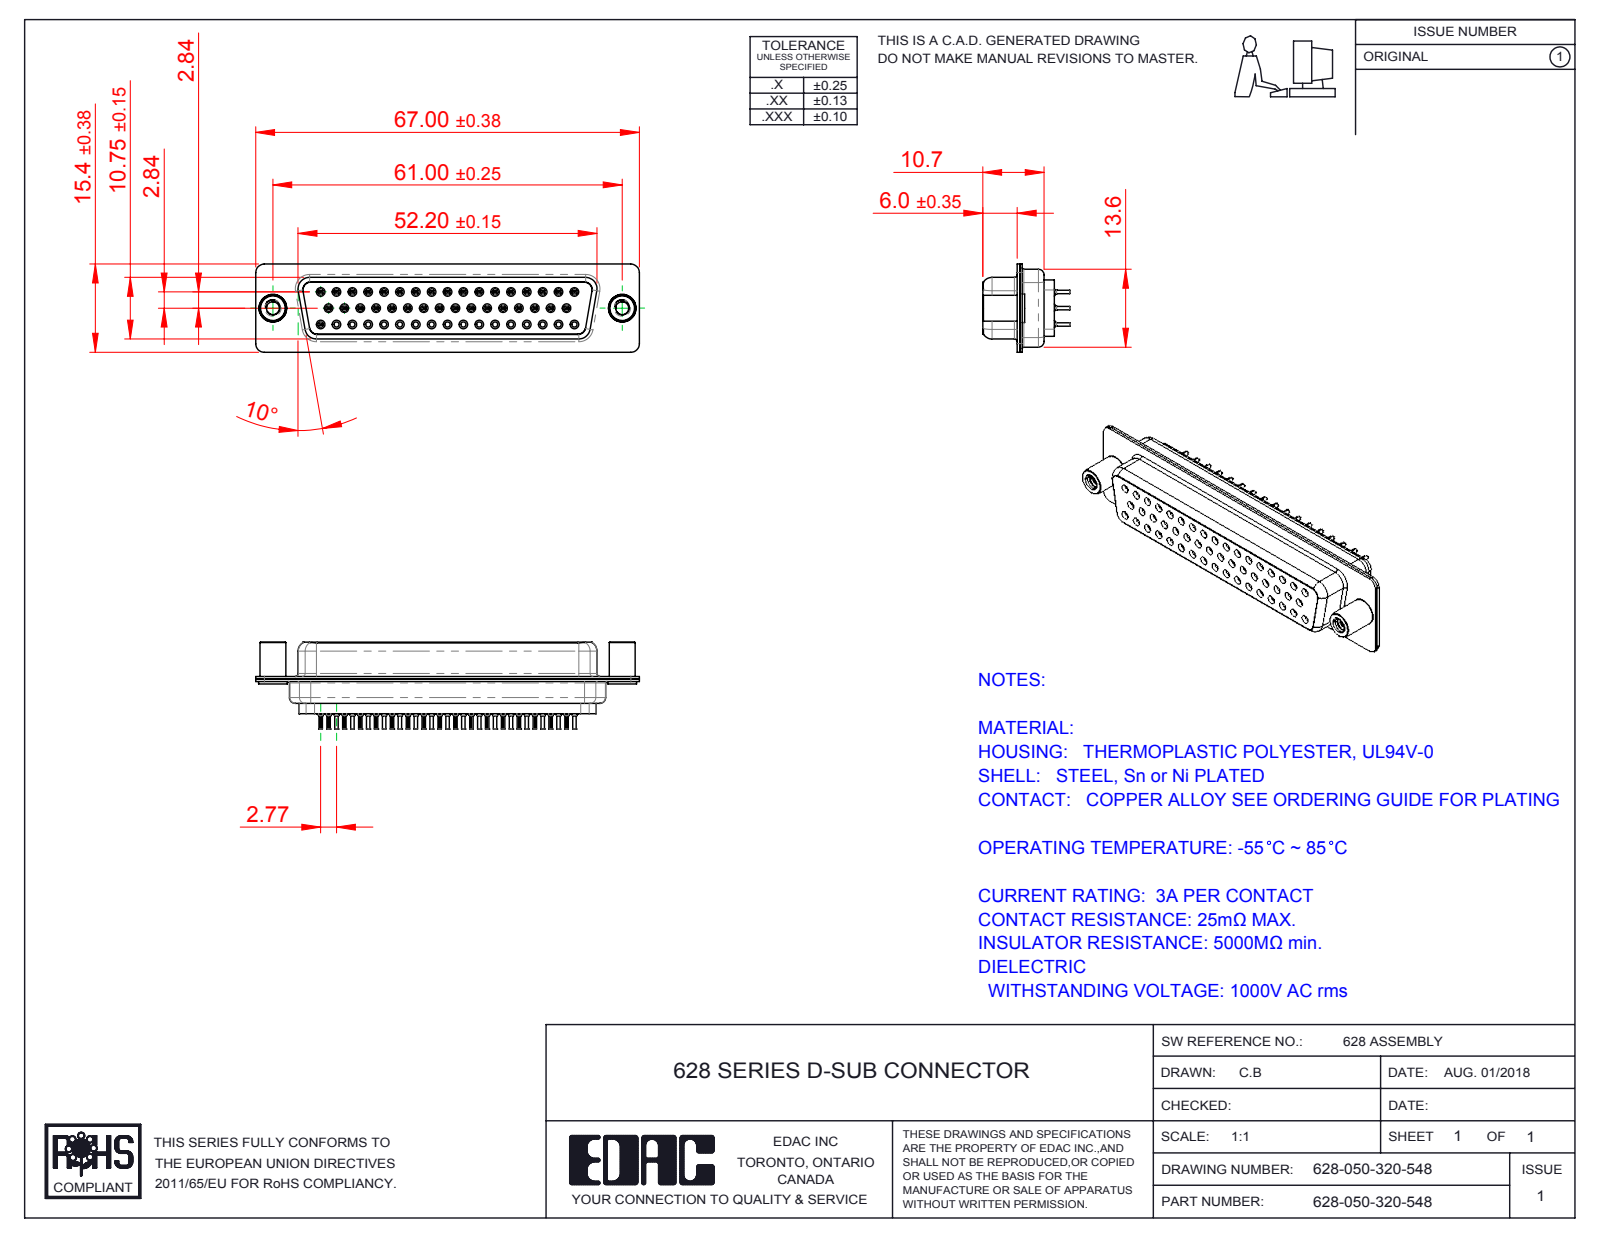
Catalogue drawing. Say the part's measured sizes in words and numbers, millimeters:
The part is named "628 Shell Rear_50 Contacts; 628 Contact Row 3_20L; 628-050-320-548; 628 Contact Row 1_20L (+4 more)". Its 3-D file was written by "SolidWorks 2016 (CONFIG_CONTROL_DESIGN)". It is 39 solids with 4839 faces: 1171 planar, 1415 cylindrical and 2253 other. Overall it measures 67 by 15.4 by 15.2 millimeters. Its volume is 6 643 cubic millimeters and its surface area 13 786 square millimeters. Round holes: 50 of diameter 0.9, 50 of diameter 1.6, 34 of diameter 0.2, 34 of diameter 0.8, 34 of diameter 1.1, 17 of diameter 1.7, 16 of diameter 1.5, 16 of diameter 2, 2 of diameter 2.26, 2 of diameter 4, 2 of diameter 4.8. Round bosses or shafts: 34 of diameter 2, 34 of diameter 1.5, 34 of diameter 1.2, 34 of diameter 0.6, 2 of diameter 5, 2 of diameter 4.9, 2 of diameter 4.5. Partial cylindrical surfaces (rounded edges, fillets, slot ends): 68 of radius 0.1, 33 of radius 0.28, 16 of radius 1.5, 12 of radius 2, 8 of radius 1.35, 4 of radius 0.25, 4 of radius 0.5, 4 of radius 0.6. The main face-to-face distances are 0.45, 0.4, 0.9, 10.3, 6.05, 6.5, 6.45, 6, 12.5, 11.33. The hole center spacings are 3.16, 2.77, 5.54, 8.31, 11.08, 13.85, 16.62, 19.39.
